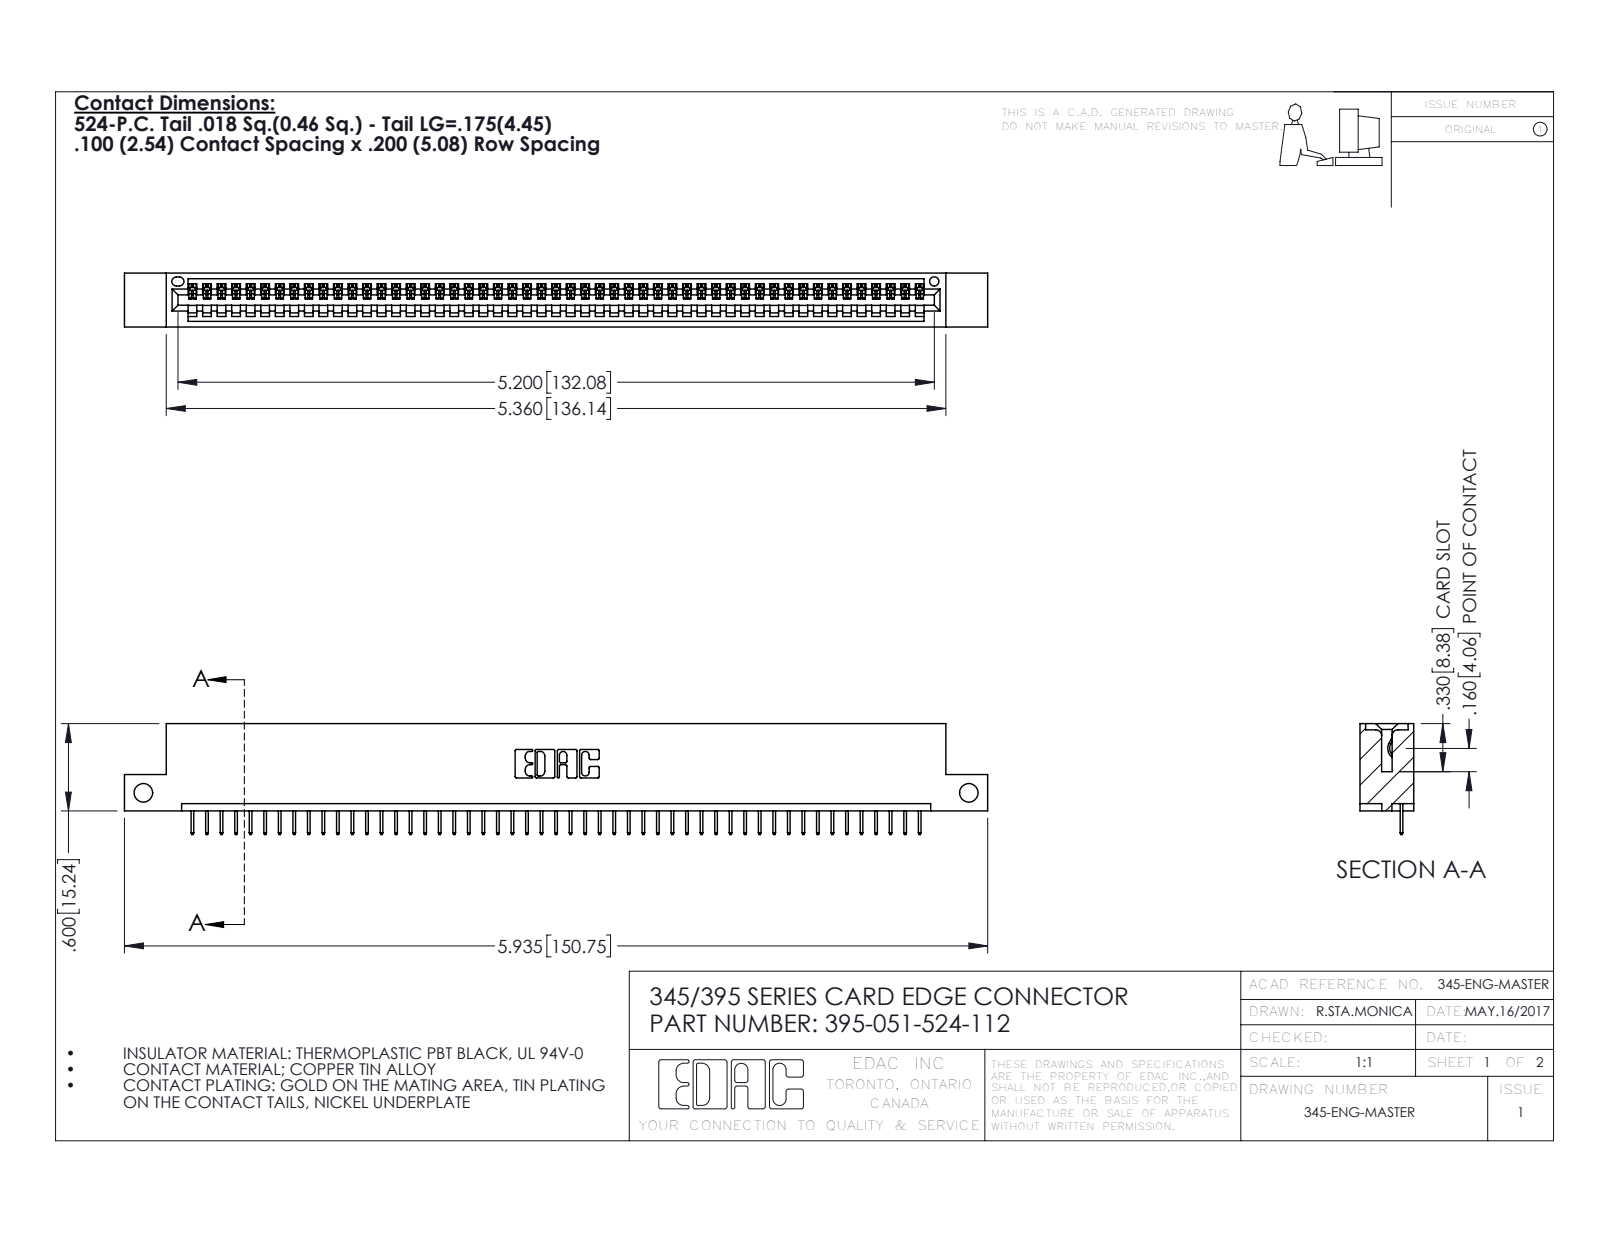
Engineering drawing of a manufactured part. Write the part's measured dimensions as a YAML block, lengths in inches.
part_name: "345-292-001_345-293-124; 345 Part_Flush Mounting Lugs - Side Mount; 395-051-524-112"
step_written_by: "SolidWorks 2016 (CONFIG_CONTROL_DESIGN)"
units: inches
bodies: {solids: 52, faces: 3288, planar: 2426, cylindrical: 862, other: 0}
overall_size: [5.935, 0.762, 0.37]
volume: 0.861
surface_area: 28.02
round_holes:
  - {diameter: 0.128, count: 2}
  - {diameter: 0.064, count: 1}
partial_cylinders:
  - {radius: 0.006, count: 102}
  - {radius: 0.01, count: 22}
  - {radius: 0.007, count: 6}
  - {radius: 0.031, count: 6}
  - {radius: 0.026, count: 3}
  - {radius: 0.031, count: 2}
  - {radius: 0.04, count: 2}
  - {radius: 0.014, count: 1}
face_to_face_distances: [0.298, 0.072, 0.37, 0.2, 0.098, 0.272, 0.025, 0.225, 0.072, 0.149]
hole_center_spacings: [5.675]
